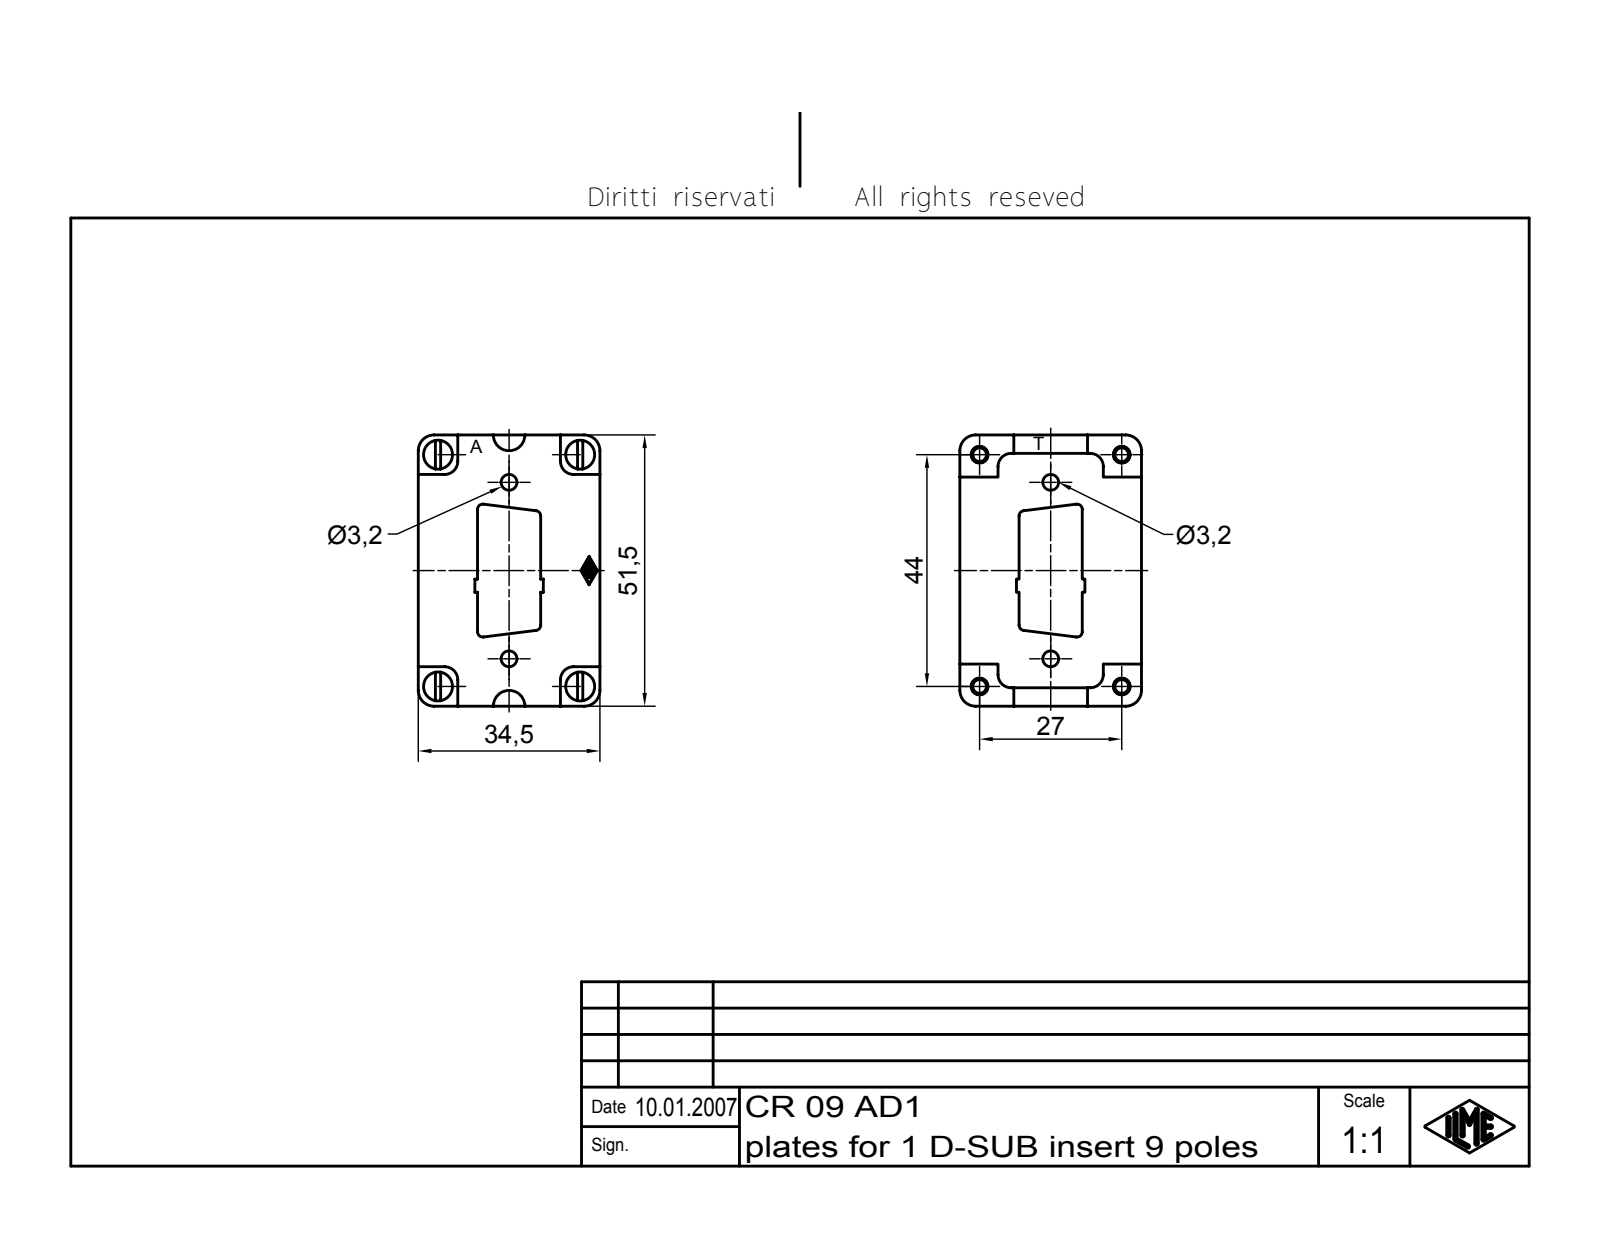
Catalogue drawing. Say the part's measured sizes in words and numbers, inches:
The part is named "CR 09 AD1". Its 3-D file was written by "Autodesk Inventor 7 (AUTOMOTIVE_DESIGN)". It is 1 solid with 195 faces: 117 planar, 62 cylindrical and 16 other. Overall it measures 2.028 by 1.358 by 0.551 inches. Its volume is 0.401 cubic inches and its surface area 9.037 square inches. Round holes: 4 of diameter 0.126, 2 of diameter 0.118. Round bosses or shafts: 4 of diameter 0.217, 4 of diameter 0.118. Partial cylindrical surfaces (rounded edges, fillets, slot ends): 14 of radius 0.004, 8 of radius 0.098, 6 of radius 0.118, 4 of radius 0.039. The main face-to-face distances are 0.118, 0.315, 0.276, 0.079, 0.394, 2.028, 0.039, 1.713, 1.358, 0.138. The hole center spacings are 0.57, 0.57, 1.063, 1.615, 1.616, 1.732, 2.032, 1.319.
